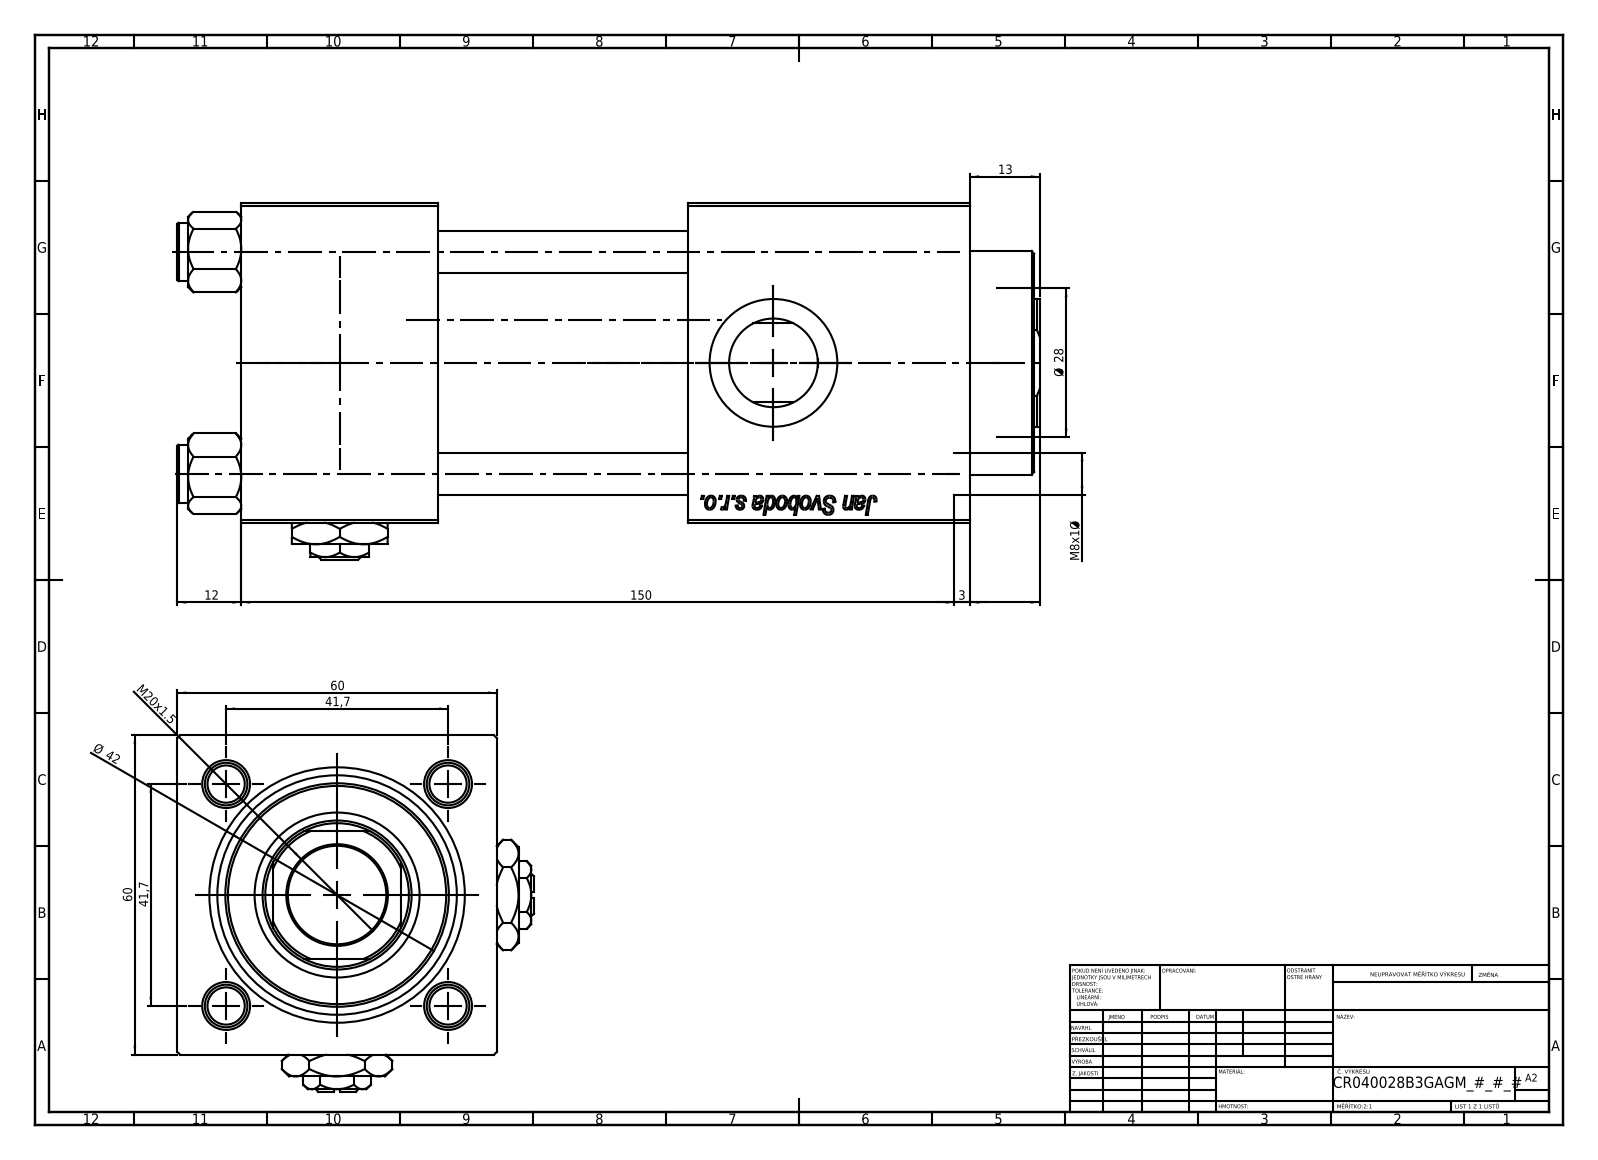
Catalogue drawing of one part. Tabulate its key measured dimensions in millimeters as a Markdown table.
| quantity | value |
| --- | --- |
| part name | NUT_M5_B; V215CR_B-1; V215_VC_A; Zatka_pro_OIL_PORT (+2 more) |
| STEP written by | SolidWorks 2019 (CONFIG_CONTROL_DESIGN) |
| units | millimeters |
| bodies | 13 solids, 1260 faces (480 planar, 90 cylindrical, 690 other) |
| overall size | 162 × 67 × 67 |
| volume | 396 104 mm³ |
| surface area | 112 639 mm² |
| round holes (diameter × count) | 8 × 4, 7 × 2, 16.66 × 2, 24 × 2, 16 × 1, 18.5 × 1, 28 × 1, 31 × 1, 40 × 1, 45 × 1 |
| round bosses / shafts (diameter × count) | 11 × 4, 46 × 1, 42 × 1 |
| partial cylindrical surfaces (radius × count) | 13.5 × 1 |
| main face-to-face distances | 60, 37, 47, 84, 137, 108.3, 71.3, 24.3, 53, 100 |
| hole center spacings | 29.49, 41.7, 58.97 |
